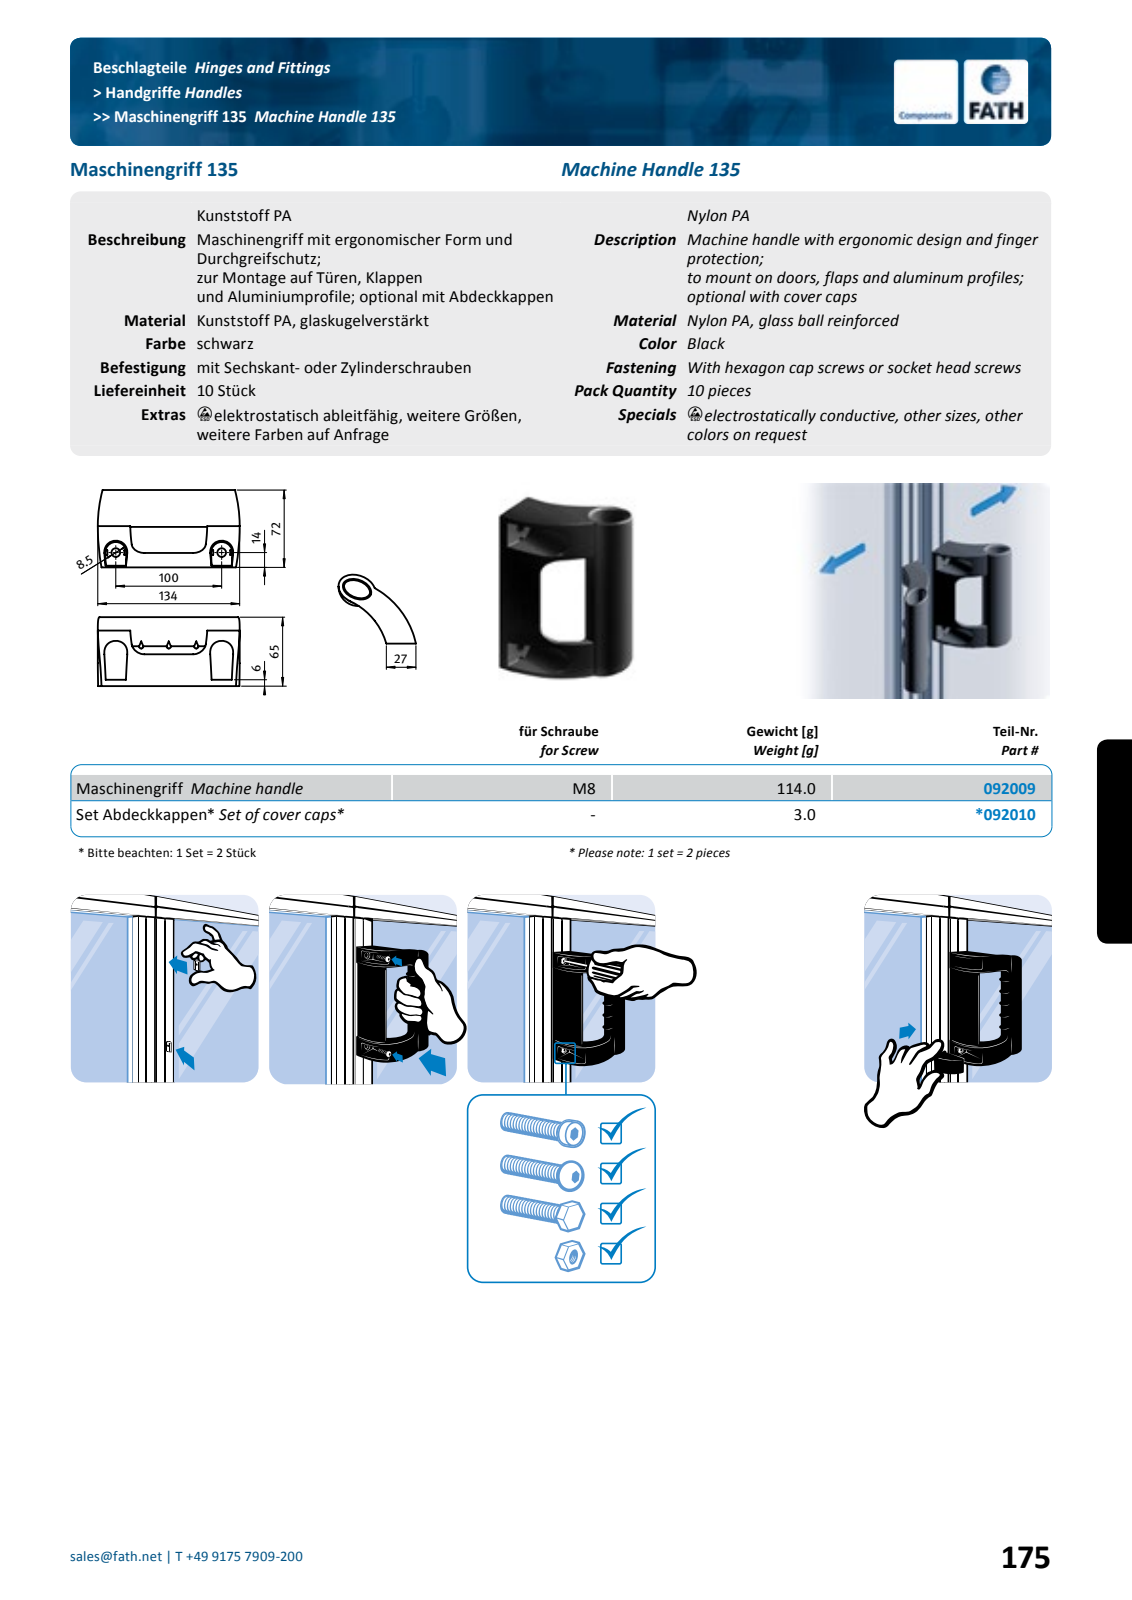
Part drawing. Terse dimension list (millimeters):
name: fath_092010
written by: Spatial InterOp 3D (automotive_design)
unit: mm
bodies: 1 solid, 62 faces (20 planar, 24 cylindrical, 18 other)
size: 35.56 × 22.52 × 21
volume: 2 404 mm³; area: 2 303 mm²
rounds: 11× R0.5, 2× R0.58, 2× R1, 2× R10, 1× R77.5, 1× R80
face distances: 1.5, 8, 13, 5, 21, 4
